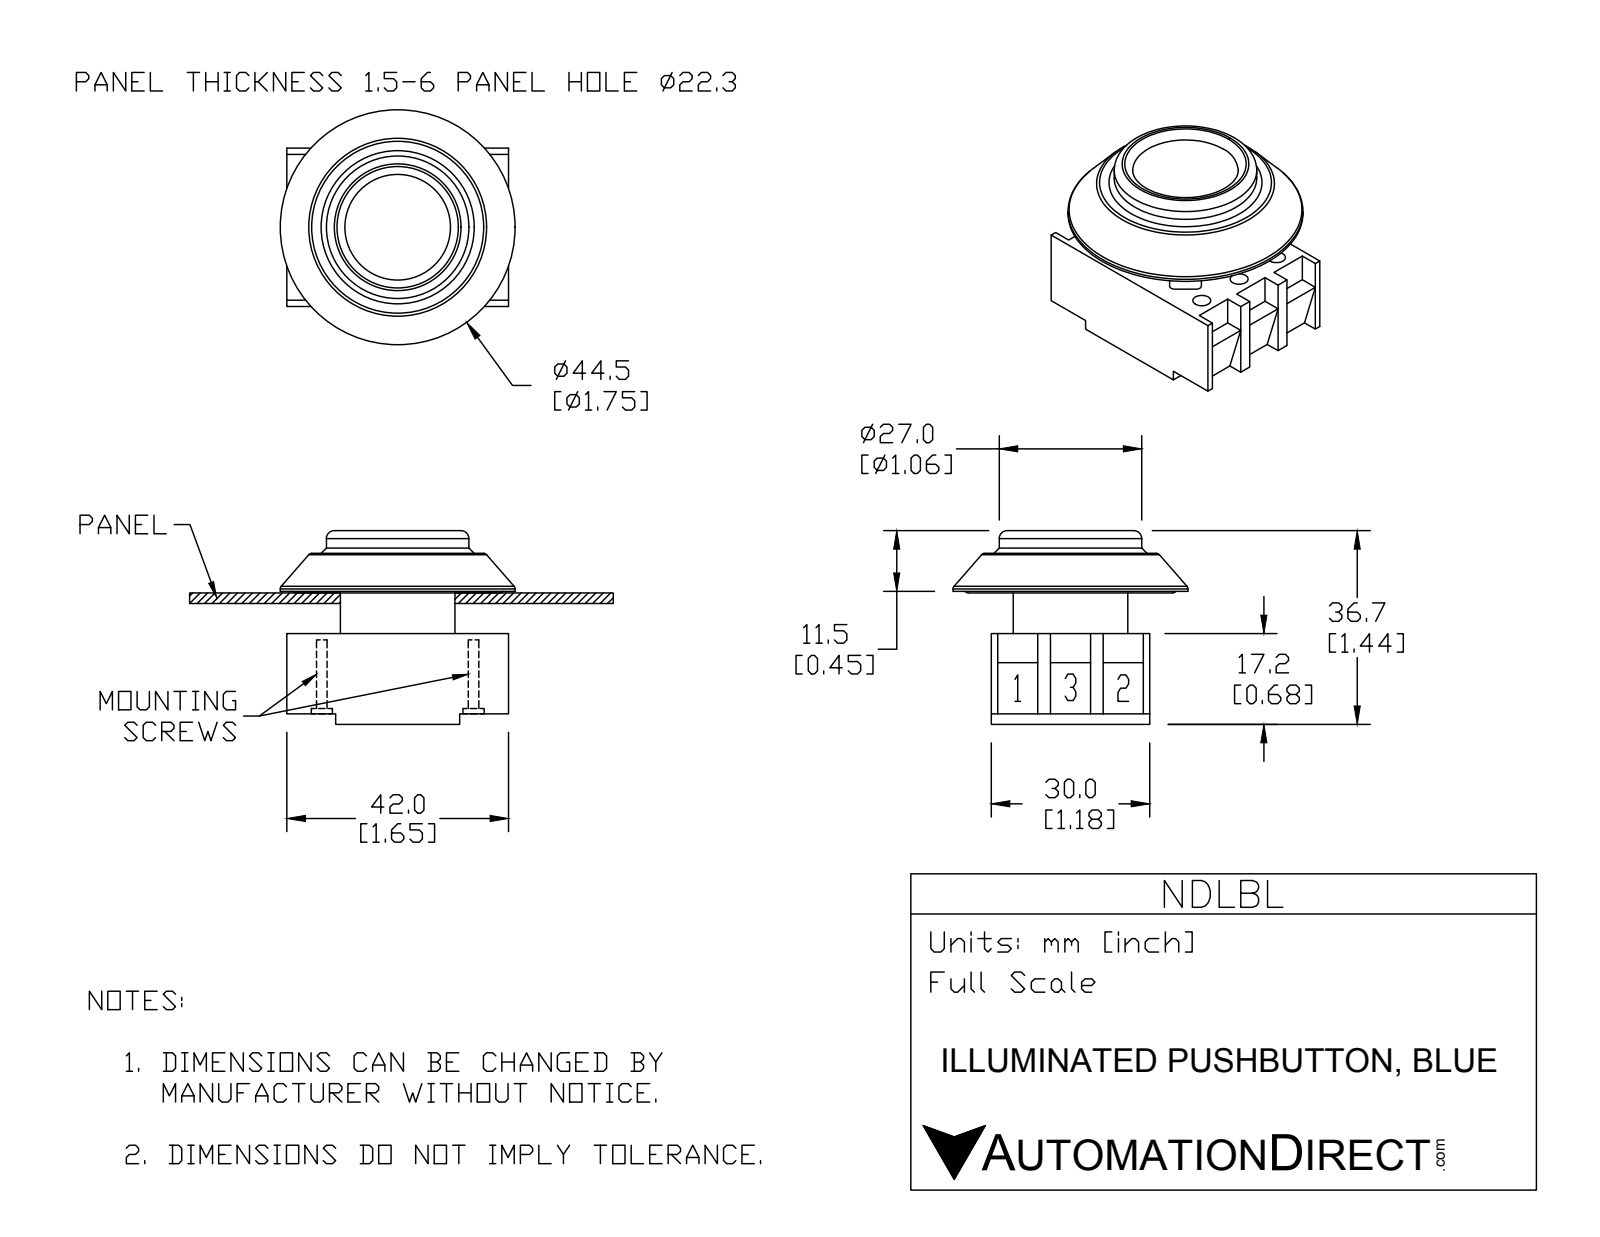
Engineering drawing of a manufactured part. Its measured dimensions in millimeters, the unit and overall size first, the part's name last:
Units: millimetres
Overall size (bounding box): 116.7 × 44.5 × 44.5
Round holes (diameter × count): ⌀3.4 ×6, ⌀5 ×6, ⌀12.5 ×1
Round bosses / shafts (diameter × count): ⌀4.6 ×2, ⌀4 ×2, ⌀44.5 ×1, ⌀27 ×1, ⌀21.7 ×1
Partial cylindrical surfaces — rounded edges, fillets, slot ends (radius × count): R1 ×8, R8.7 ×5, R11 ×1
Main face-to-face distances: 7.2, 30, 40, 47.2, 10, 88, 48, 95.2, 47.7, 40.3
Hole centre spacings: 10, 17.52, 30.45, 28.76, 14.38, 20, 35.03
Volume: 25 120 mm³ · Surface area: 16 719 mm²
Bodies: 7 solids, 217 faces (127 planar, 65 cylindrical, 25 other)
Part name (STEP PRODUCT): NDLBL
STEP written by: SolidWorks 2015 (AUTOMOTIVE_DESIGN)
